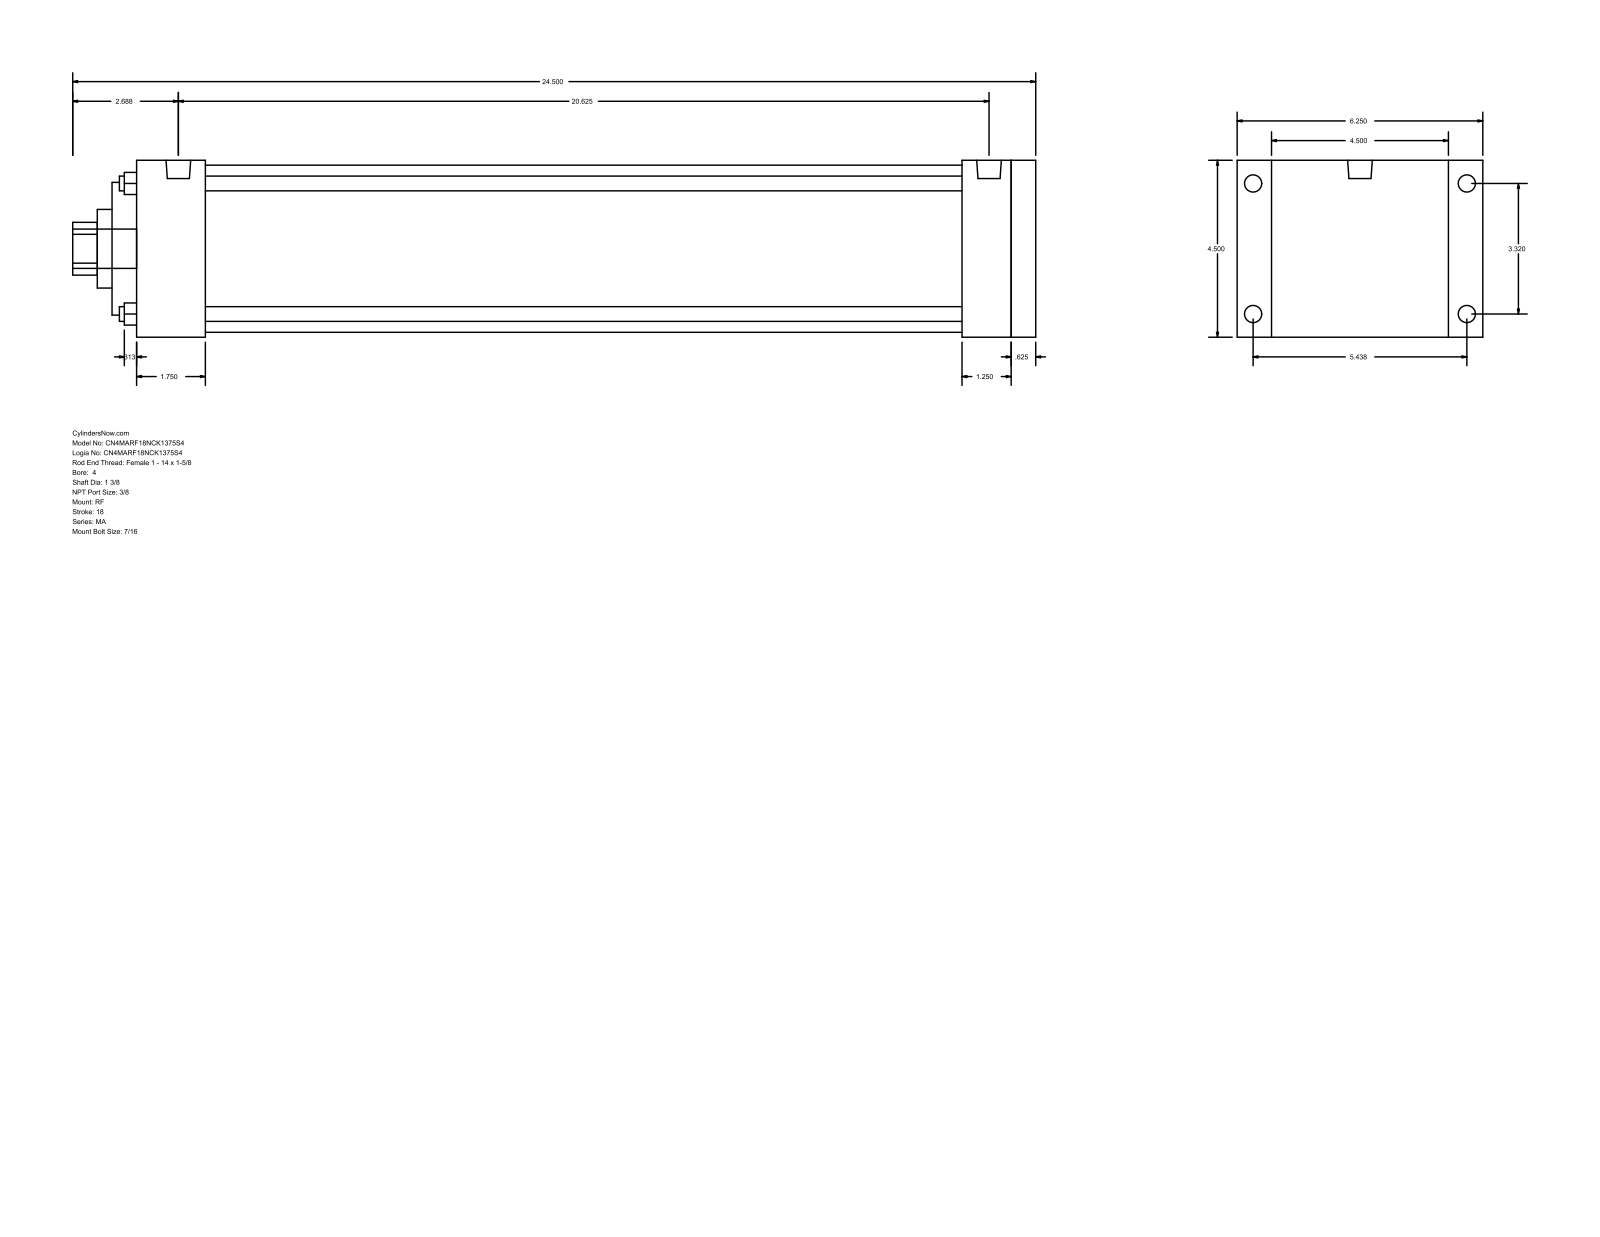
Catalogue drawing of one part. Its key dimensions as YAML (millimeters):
part_name: "MA_RF__0400_1.375"
step_written_by: "GSSL Pune (CONFIG_CONTROL_DESIGN)"
units: millimeters
bodies: {solids: 0, faces: 94, planar: 65, cylindrical: 29, other: 0}
overall_size: [622.3, 158.75, 114.3]
round_holes:
  - {diameter: 9.53, count: 4}
  - {diameter: 34.92, count: 1}
  - {diameter: 50.8, count: 1}
  - {diameter: 85.72, count: 1}
  - {diameter: 107.95, count: 1}
round_bosses_or_shafts:
  - {diameter: 11.11, count: 8}
  - {diameter: 15.93, count: 2}
  - {diameter: 25.4, count: 1}
partial_cylinders:
  - {radius: 17.06, count: 1}
face_to_face_distances: [114.3, 581.03, 15.88, 565.15, 15.87, 581.02, 596.9, 22.23, 136.53, 549.27]
hole_center_spacings: [59.62, 84.32, 119.25]
